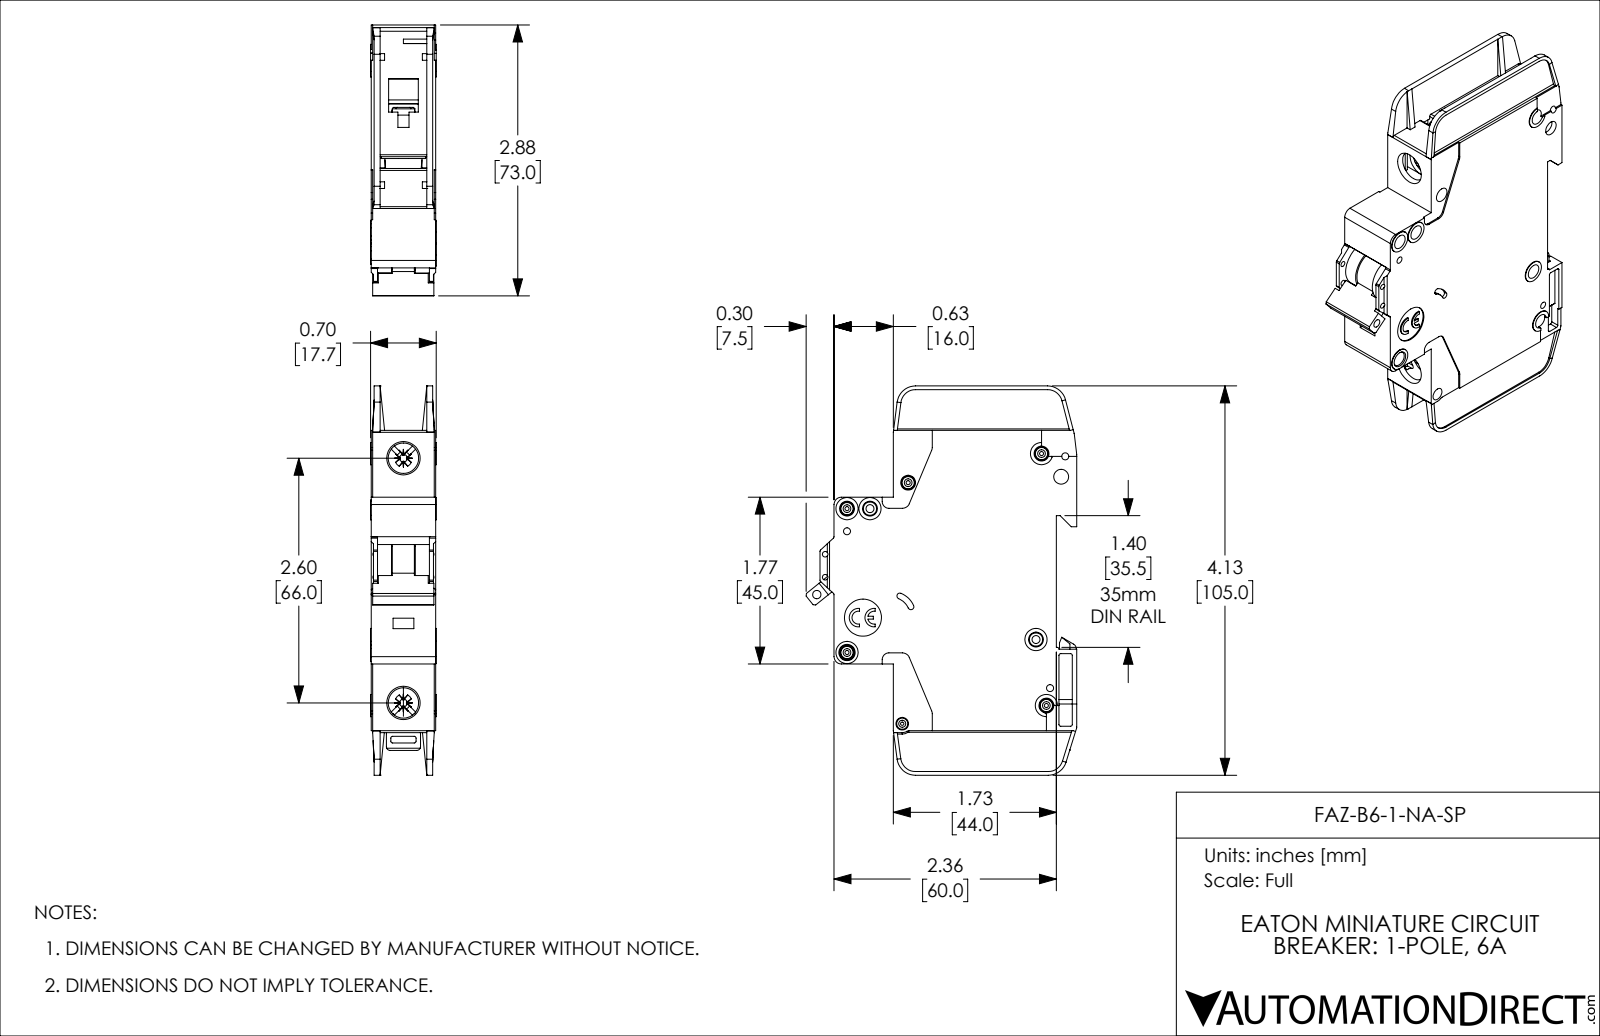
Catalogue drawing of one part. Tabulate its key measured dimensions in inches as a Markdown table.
| quantity | value |
| --- | --- |
| part name | FAZ-B6-1-NA-SP |
| STEP written by | SolidWorks 2019 (AUTOMOTIVE_DESIGN) |
| units | inches |
| bodies | 1 solid, 1127 faces (671 planar, 357 cylindrical, 99 other) |
| overall size | 4.134 × 2.876 × 0.697 |
| volume | 4.682 in³ |
| surface area | 41.01 in² |
| round holes (diameter × count) | 0.157 × 8, 0.043 × 5, 0.075 × 4, 0.059 × 2, 0.085 × 2, 0.323 × 2, 0.035 × 1, 0.089 × 1, 0.098 × 1, 0.134 × 1, 0.394 × 1 |
| round bosses / shafts (diameter × count) | 0.13 × 5, 0.236 × 4, 0.118 × 2, 0.098 × 1 |
| partial cylindrical surfaces (radius × count) | 0.02 × 42, 0.016 × 10, 0.039 × 10, 0.079 × 8, 0.197 × 5, 0.008 × 4, 0.026 × 4, 0.043 × 4 |
| main face-to-face distances | 0.047, 0.685, 0.591, 0.638, 0.094, 0.543, 0.016, 0.031, 0.496, 0.575 |
| hole center spacings | 0.244, 0.537, 0.87, 0.189, 0.199, 0.204, 0.221, 0.24 |
